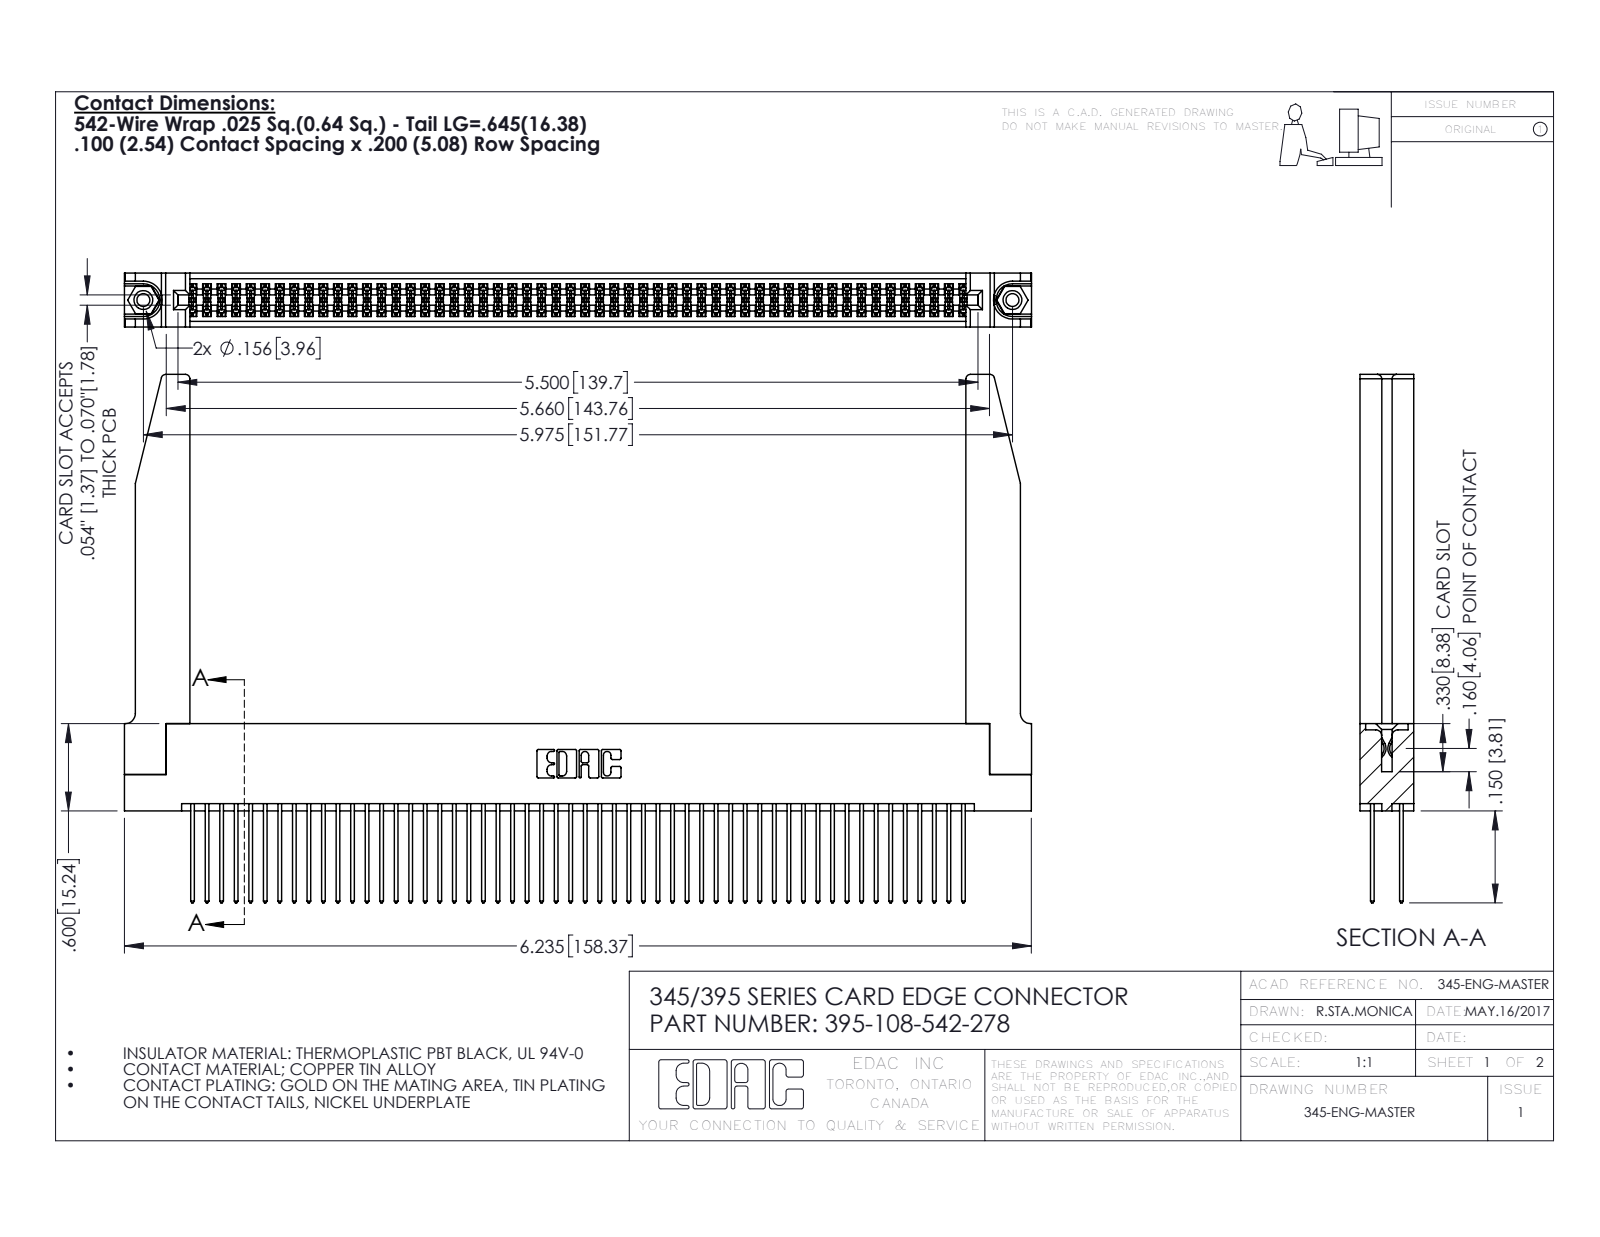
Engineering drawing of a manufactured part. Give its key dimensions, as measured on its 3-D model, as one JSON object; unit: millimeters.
{"part_name": "345-220-078_345-220-078; 345-292-001_345-293-142; 345 Part_Flush Mounting Lugs - 0.156 Dia-TH; 345-250-001_345-250-001-102 (+1 more)", "step_written_by": "SolidWorks 2016 (CONFIG_CONTROL_DESIGN)", "units": "millimeters", "bodies": {"solids": 113, "faces": 5760, "planar": 3786, "cylindrical": 1922, "other": 52}, "overall_size": [158.4, 92.3, 9.4], "volume_mm3": 23780, "surface_area_mm2": 33080, "round_holes": [[2.3, 2], [3.2, 2], [4, 2], [1.6, 1]], "round_bosses_or_shafts": [[3.9, 2]], "partial_cylinders_radius": [[0.2, 162], [0.3, 108], [0.3, 22], [0.8, 8], [0.2, 6], [0.8, 6], [0.7, 3], [0.4, 2]], "face_to_face_distances": [1.8, 7.6, 9.4, 5.1, 2.5, 6.9, 0.6, 5.7, 4.4, 3.8], "hole_center_spacings": [6.9, 145.8, 151.8]}
